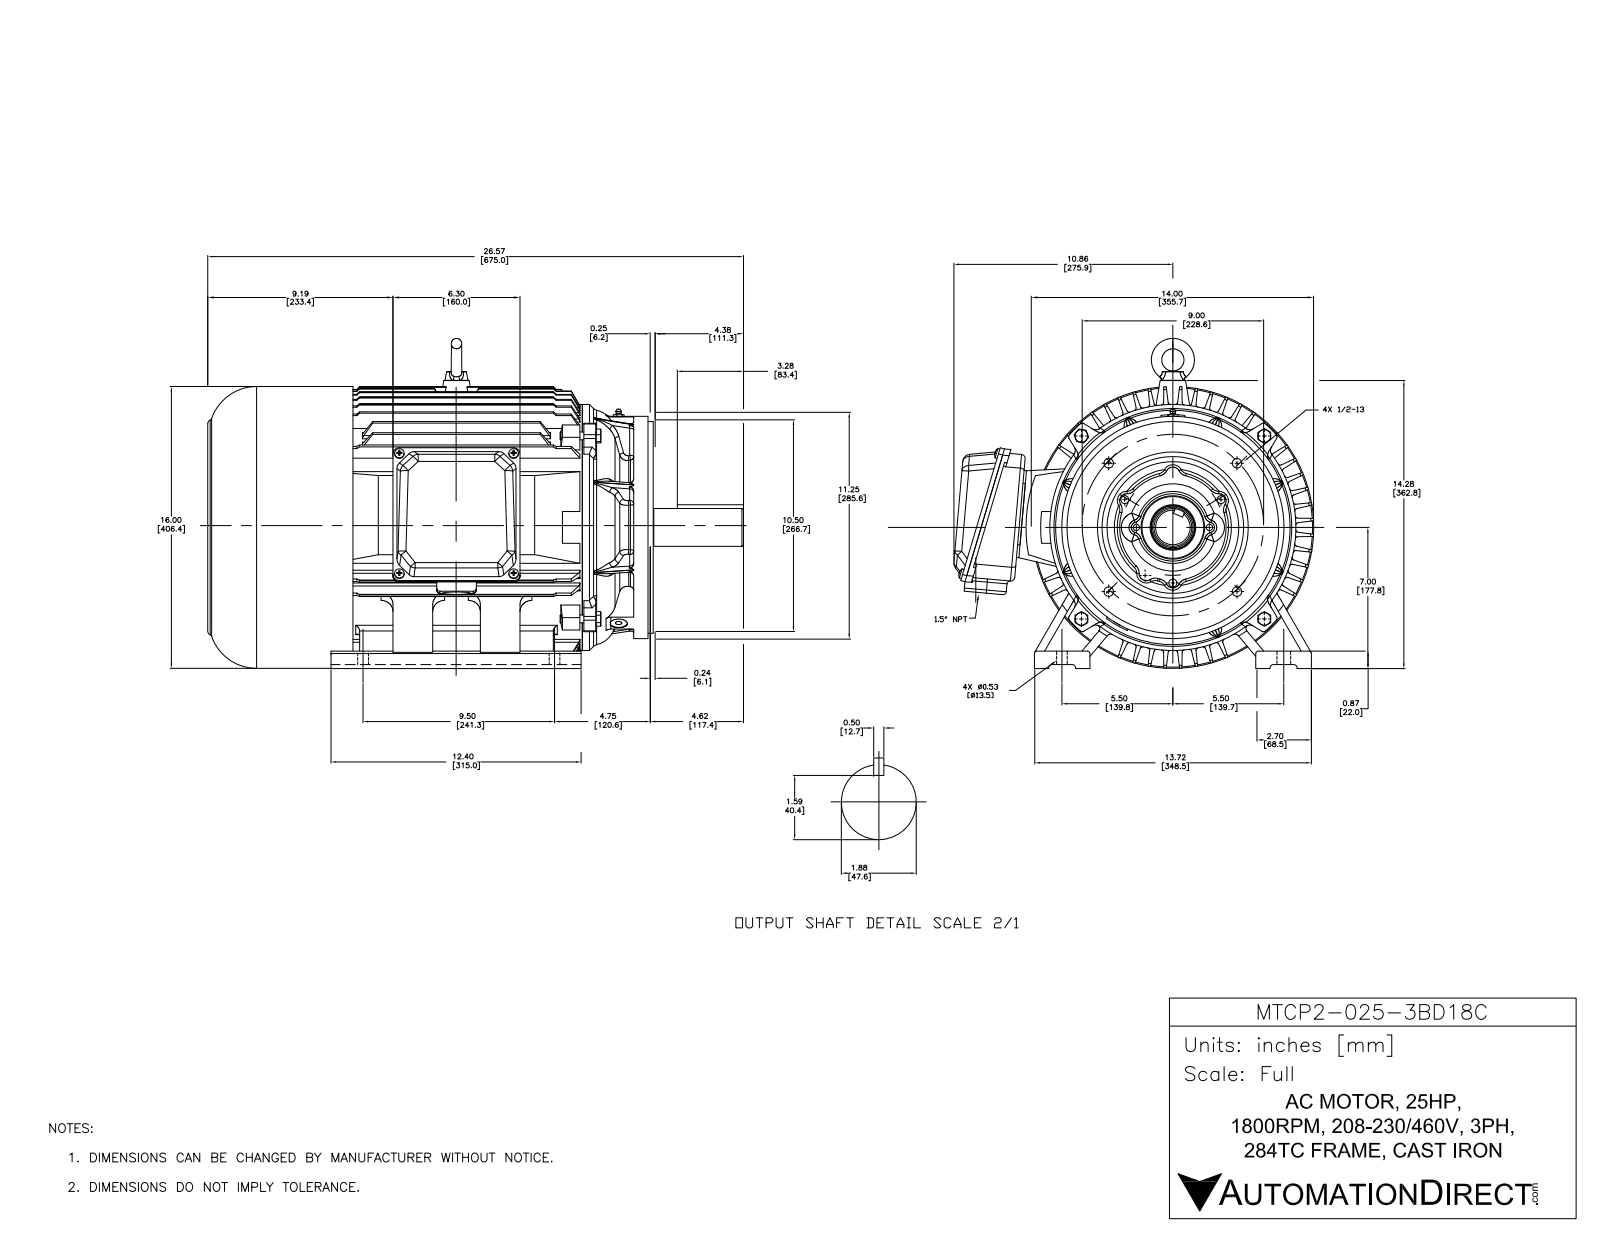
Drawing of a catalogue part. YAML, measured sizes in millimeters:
part_name: "PEWWE-284TC-4,6,8"
step_written_by: "SolidWorks 2017 (AUTOMOTIVE_DESIGN)"
units: millimeters
bodies: {solids: 20, faces: 2804, planar: 1711, cylindrical: 618, other: 475}
overall_size: [675, 453.4, 415.9]
volume: 9681000
surface_area: 2445000
round_holes:
  - {diameter: 10, count: 9}
  - {diameter: 7, count: 8}
  - {diameter: 12, count: 8}
  - {diameter: 8, count: 5}
  - {diameter: 5, count: 4}
  - {diameter: 14, count: 4}
  - {diameter: 2, count: 2}
  - {diameter: 22, count: 2}
  - {diameter: 10.2, count: 1}
  - {diameter: 17, count: 1}
  - {diameter: 36, count: 1}
  - {diameter: 55.5, count: 1}
round_bosses_or_shafts:
  - {diameter: 12, count: 5}
  - {diameter: 6, count: 4}
  - {diameter: 9.1, count: 2}
  - {diameter: 355, count: 1}
  - {diameter: 310, count: 1}
  - {diameter: 280, count: 1}
  - {diameter: 266.7, count: 1}
  - {diameter: 158, count: 1}
partial_cylinders:
  - {radius: 3, count: 72}
  - {radius: 0.5, count: 60}
  - {radius: 4, count: 56}
  - {radius: 5, count: 26}
  - {radius: 10, count: 26}
  - {radius: 0.3, count: 16}
  - {radius: 8, count: 16}
  - {radius: 12, count: 5}
face_to_face_distances: [5, 1.5, 22, 557.7, 559.2, 6, 10, 24.5, 533.2, 534.7]
hole_center_spacings: [144, 158, 199.1, 70, 213.8, 48.7, 81.5, 83.8]
